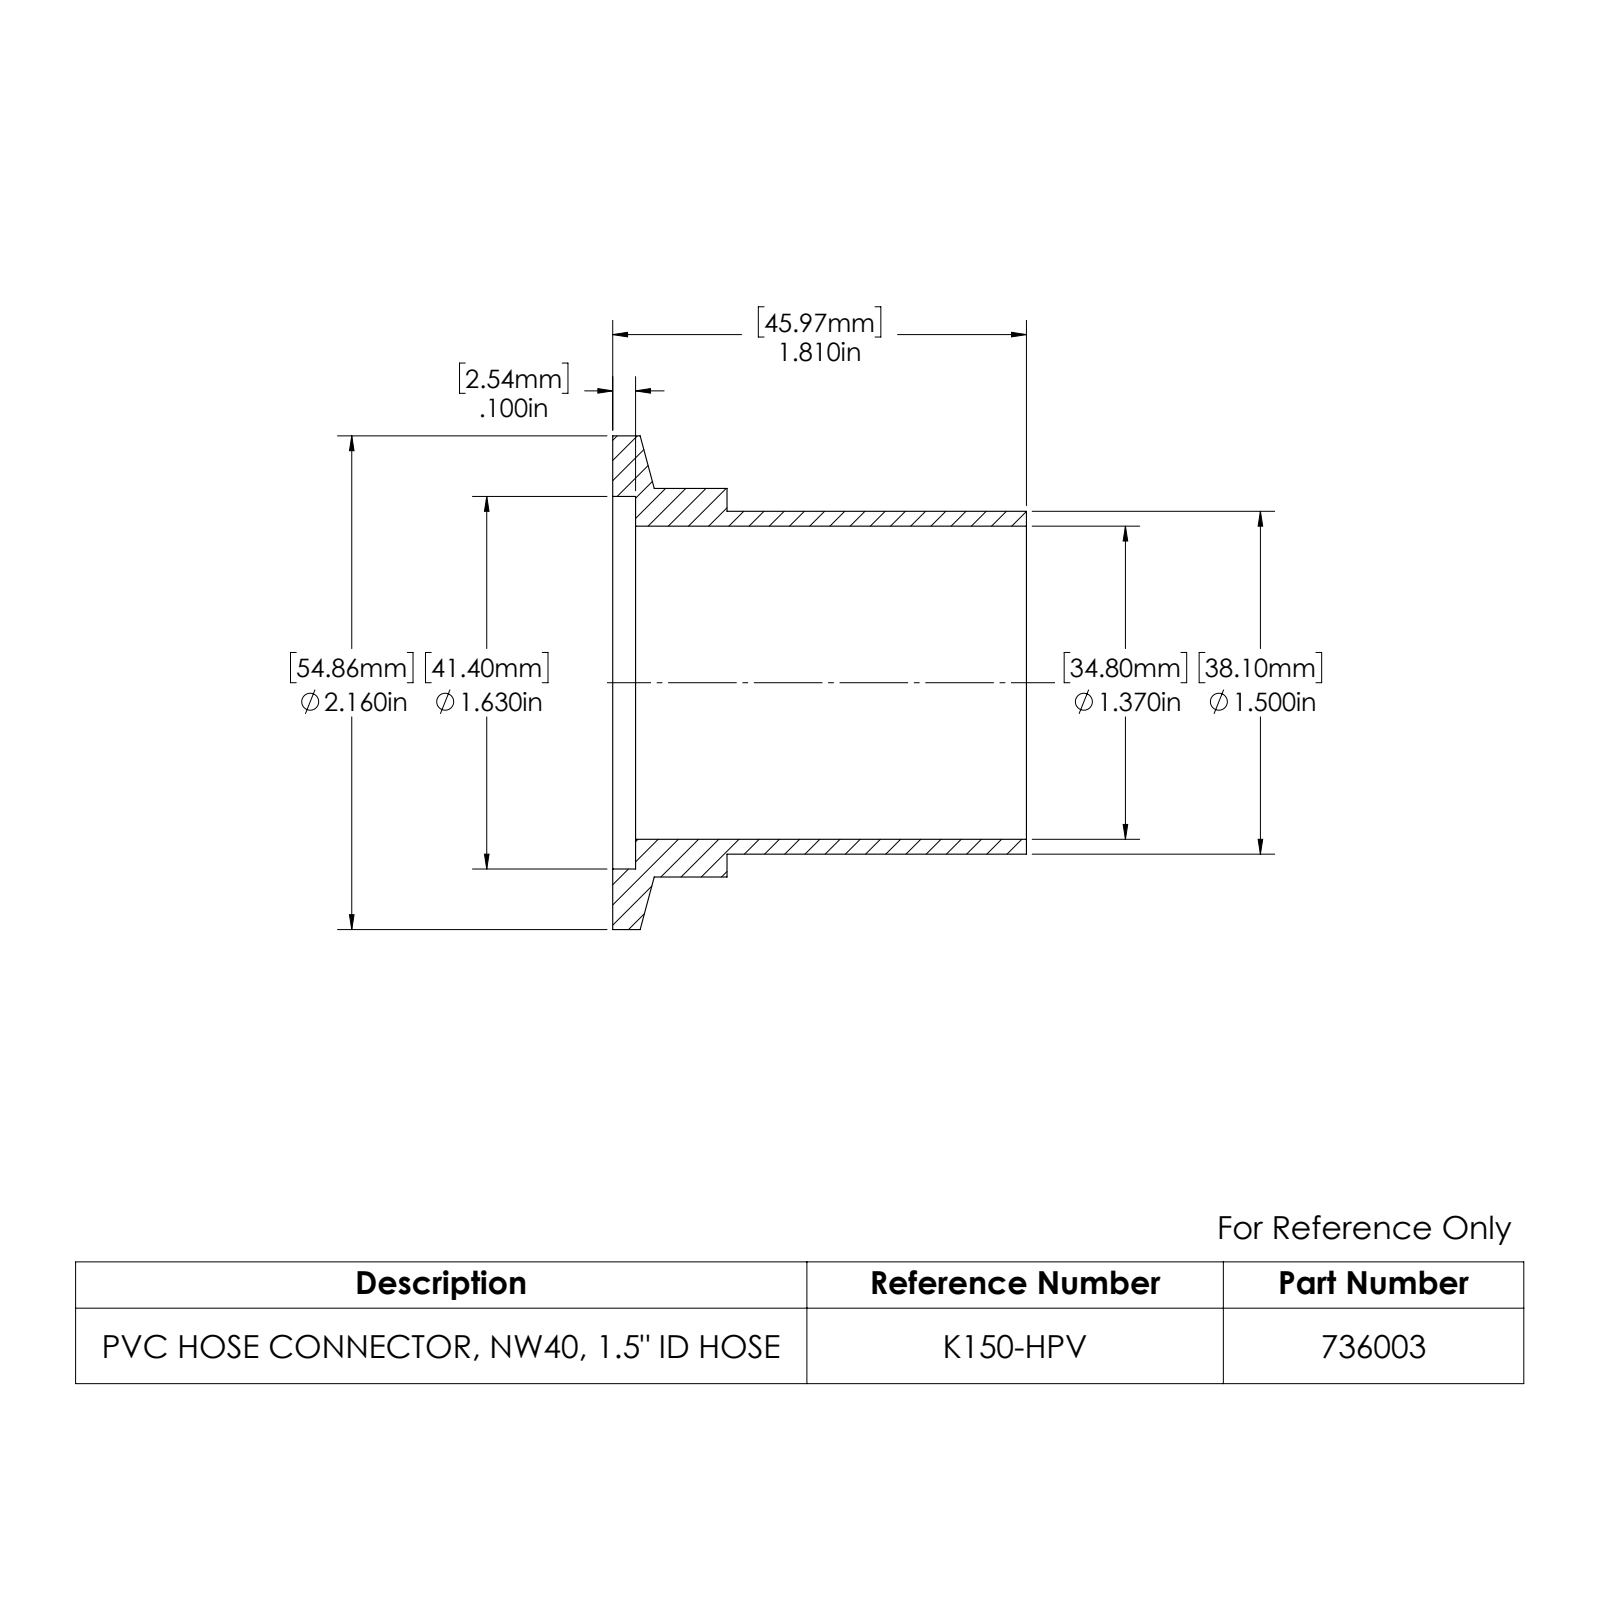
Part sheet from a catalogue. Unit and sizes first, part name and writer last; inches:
Units: inches
Overall size (bounding box): 2.16 × 2.16 × 1.81
Round holes (diameter × count): ⌀1.37 ×1, ⌀1.63 ×1
Round bosses / shafts (diameter × count): ⌀2.16 ×1, ⌀1.7 ×1, ⌀1.5 ×1
Main face-to-face distances: 0.1, 0.5, 0.4, 1.81, 1.71, 1.31
Volume: 0.929 in³ · Surface area: 20.99 in²
Bodies: 1 solid, 16 faces (4 planar, 10 cylindrical, 2 other)
Part name (STEP PRODUCT): 736003
STEP written by: SolidWorks 2022 (AUTOMOTIVE_DESIGN)
